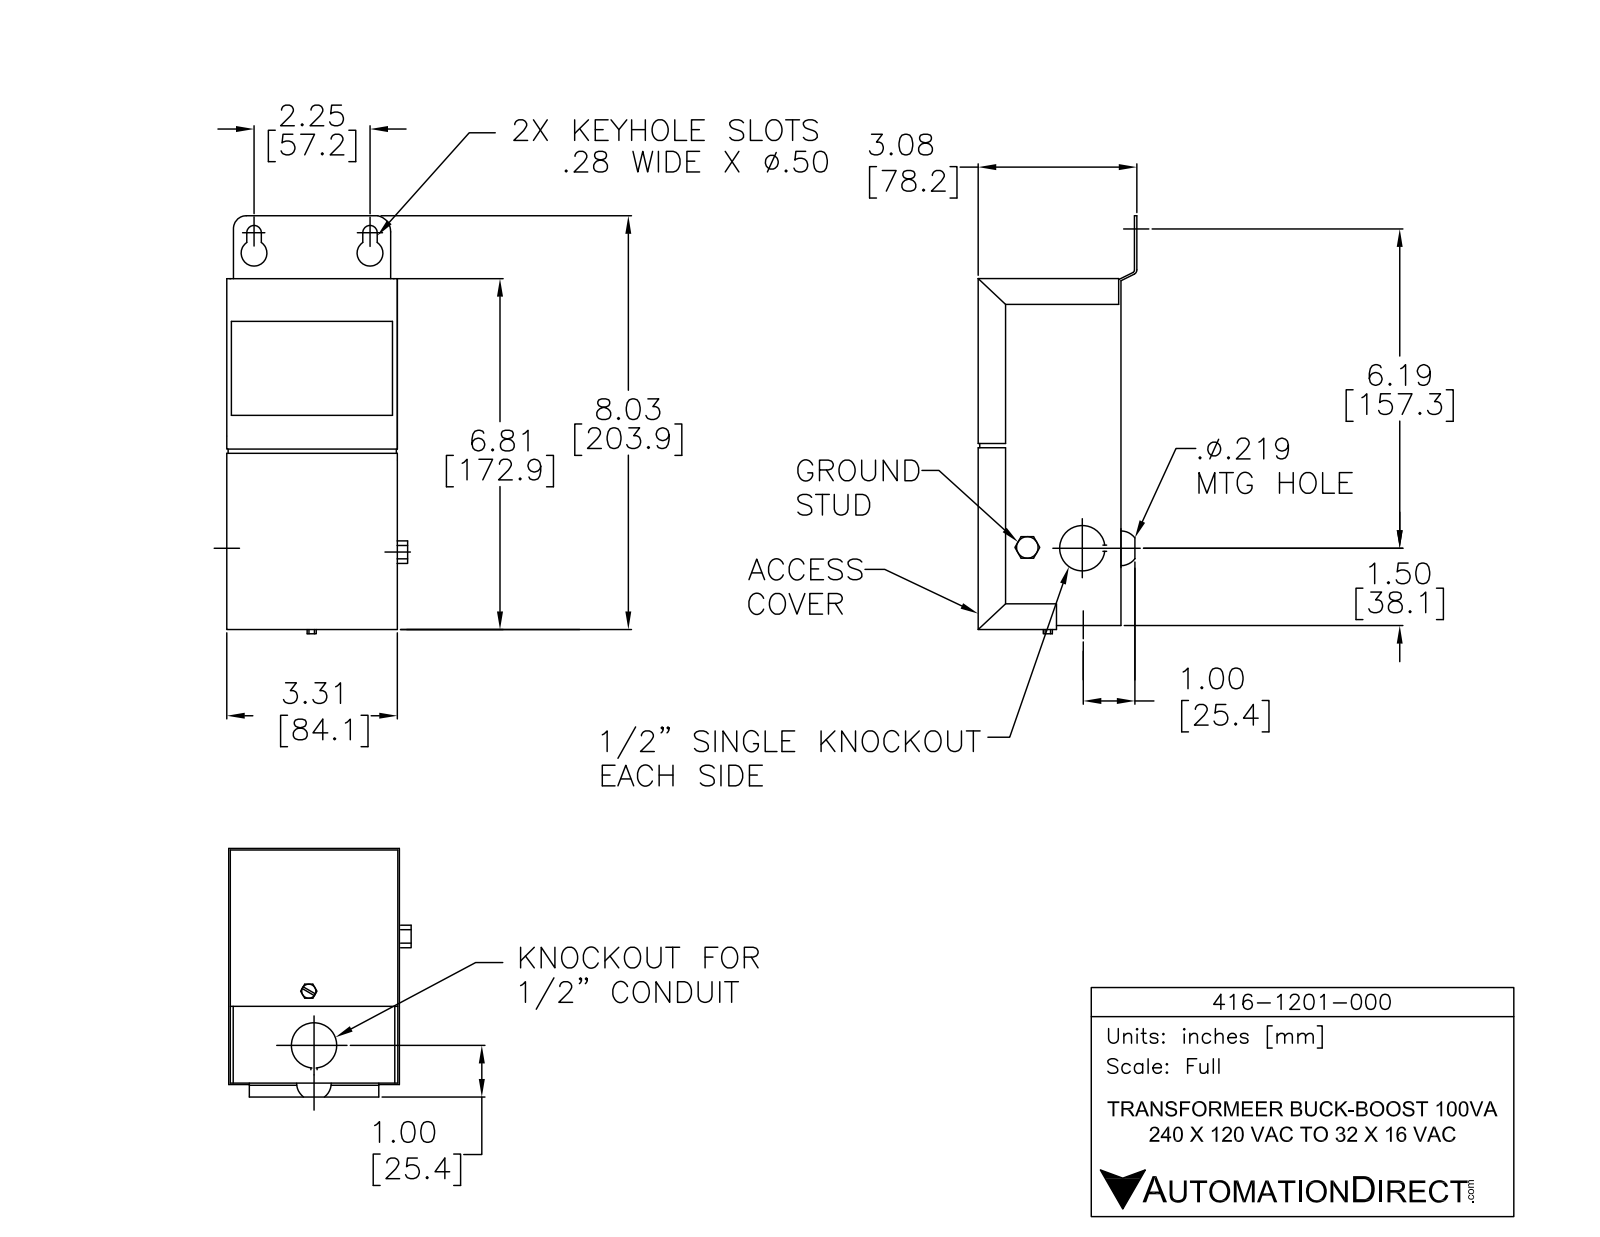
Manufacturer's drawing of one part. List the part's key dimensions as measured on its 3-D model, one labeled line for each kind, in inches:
Part name (STEP PRODUCT): 416-1201-000
STEP written by: SolidWorks 2013 (AUTOMOTIVE_DESIGN)
Units: inches
Bodies: 1 solid, 150 faces (89 planar, 45 cylindrical, 16 other)
Overall size (bounding box): 8.14 × 3.42 × 3.081
Volume: 63.4 in³ · Surface area: 112.7 in²
Round holes (diameter × count): ⌀0.5 ×2, ⌀0.875 ×2, ⌀0.185 ×1, ⌀0.231 ×1, ⌀0.275 ×1
Partial cylindrical surfaces — rounded edges, fillets, slot ends (radius × count): R0.04 ×10, R0.25 ×10, R0.14 ×2, R0.06 ×1, R0.1 ×1
Main face-to-face distances: 2.861, 3.23, 0.04, 3.27, 0.04, 2.86, 3.31, 6.81, 6.77, 0.22
Hole centre spacings: 5.908, 0.763, 0.862, 2.25
